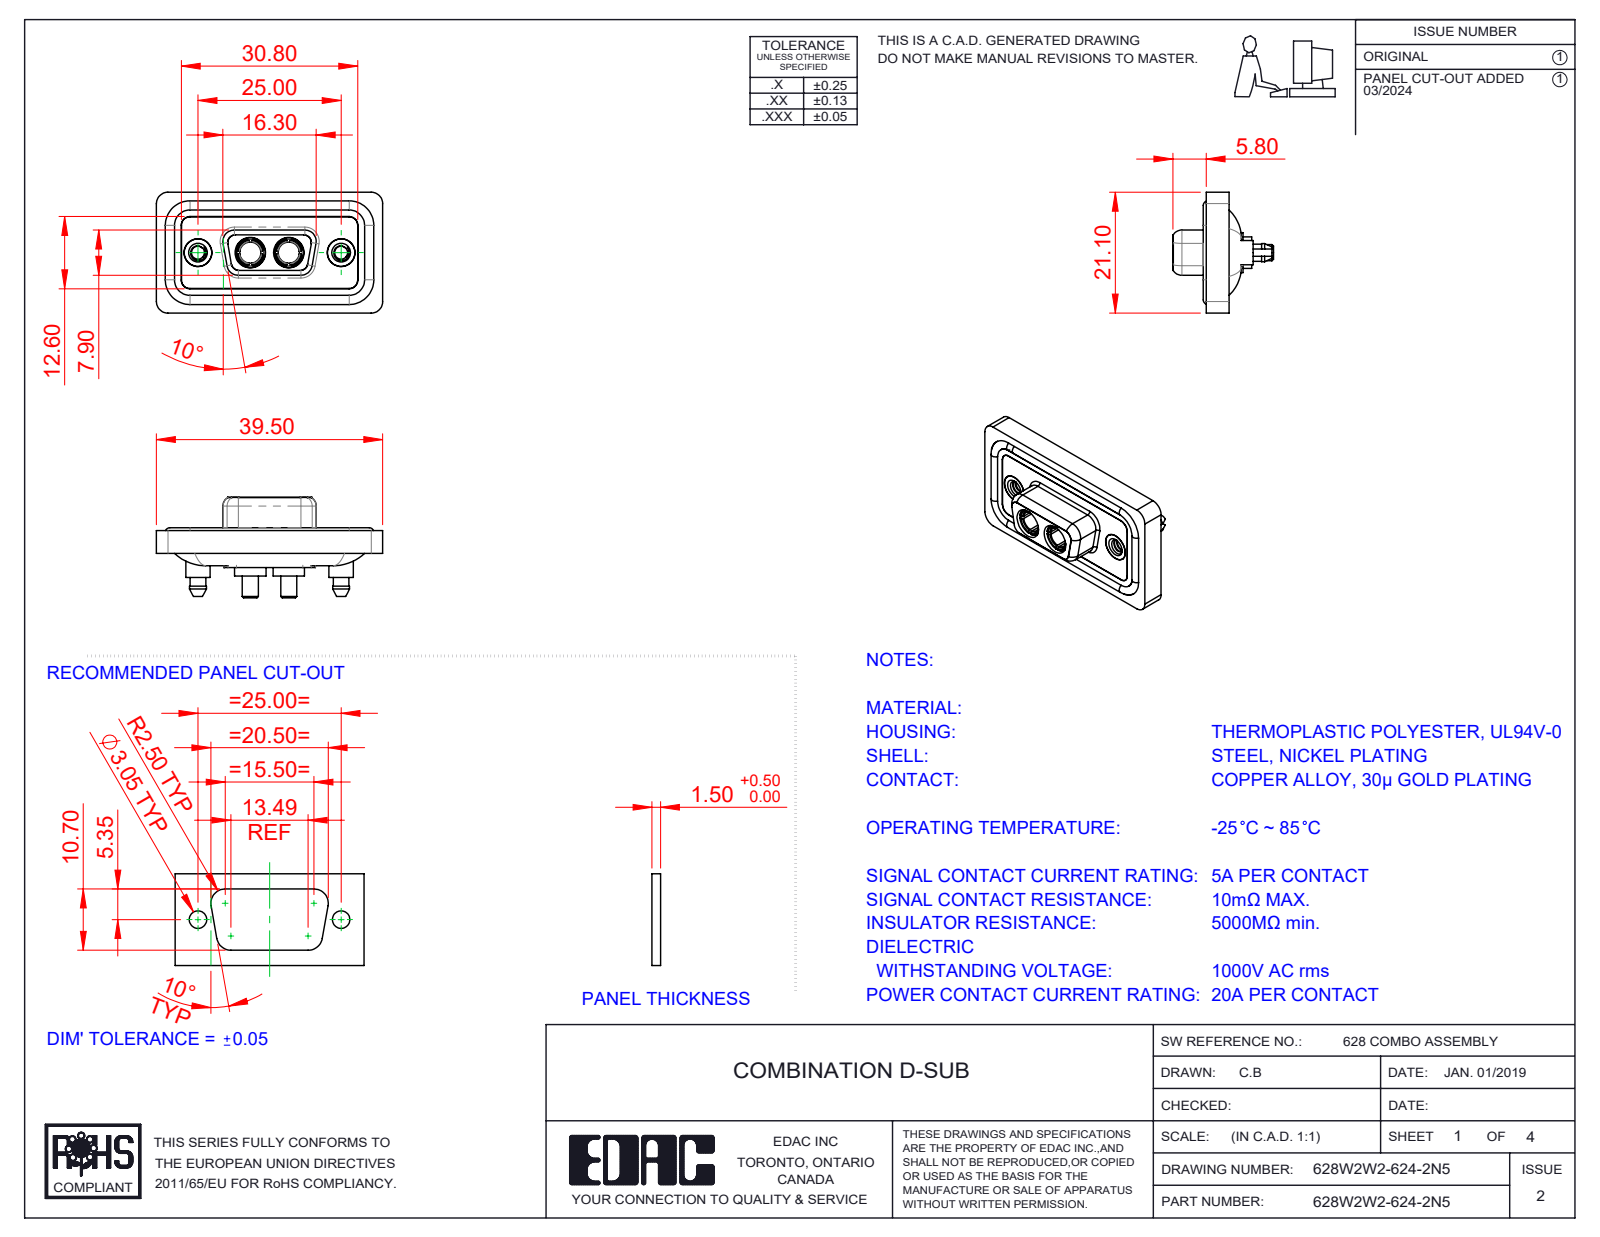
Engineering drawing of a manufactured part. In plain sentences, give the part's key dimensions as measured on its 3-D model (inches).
The part is named "628Combo Threaded Boardlock_5; 628Combo Waterproof Housing_09 Contacts; 628Combo Shell Rear_09 Contacts; 628Combo Housing_2W2 (+3 more)". Its 3-D file was written by "SolidWorks 2023 (CONFIG_CONTROL_DESIGN)". It is 11 solids with 584 faces: 179 planar, 266 cylindrical and 139 other. Overall it measures 1.555 by 0.831 by 0.691 inches. Its volume is 0.296 cubic inches and its surface area 12.35 square inches. Round holes: 4 of diameter 0.191, 2 of diameter 0.089, 2 of diameter 0.146, 2 of diameter 0.157, 2 of diameter 0.159, 2 of diameter 0.197, 2 of diameter 0.209. Round bosses or shafts: 4 of diameter 0.063, 2 of diameter 0.217, 2 of diameter 0.213, 2 of diameter 0.205, 2 of diameter 0.195, 2 of diameter 0.195, 2 of diameter 0.189, 2 of diameter 0.187. Partial cylindrical surfaces (rounded edges, fillets, slot ends): 24 of radius 0.059, 18 of radius 0.079, 10 of radius 0.063, 8 of radius 0.053, 4 of radius 0.01, 4 of radius 0.02, 4 of radius 0.024, 4 of radius 0.026. The main face-to-face distances are 0.016, 0.071, 0.043, 0.114, 0.063, 0.02, 0.222, 0.293, 0.059, 0.157. The hole center spacings are 0.36, 0.624, 0.265, 0.984.
